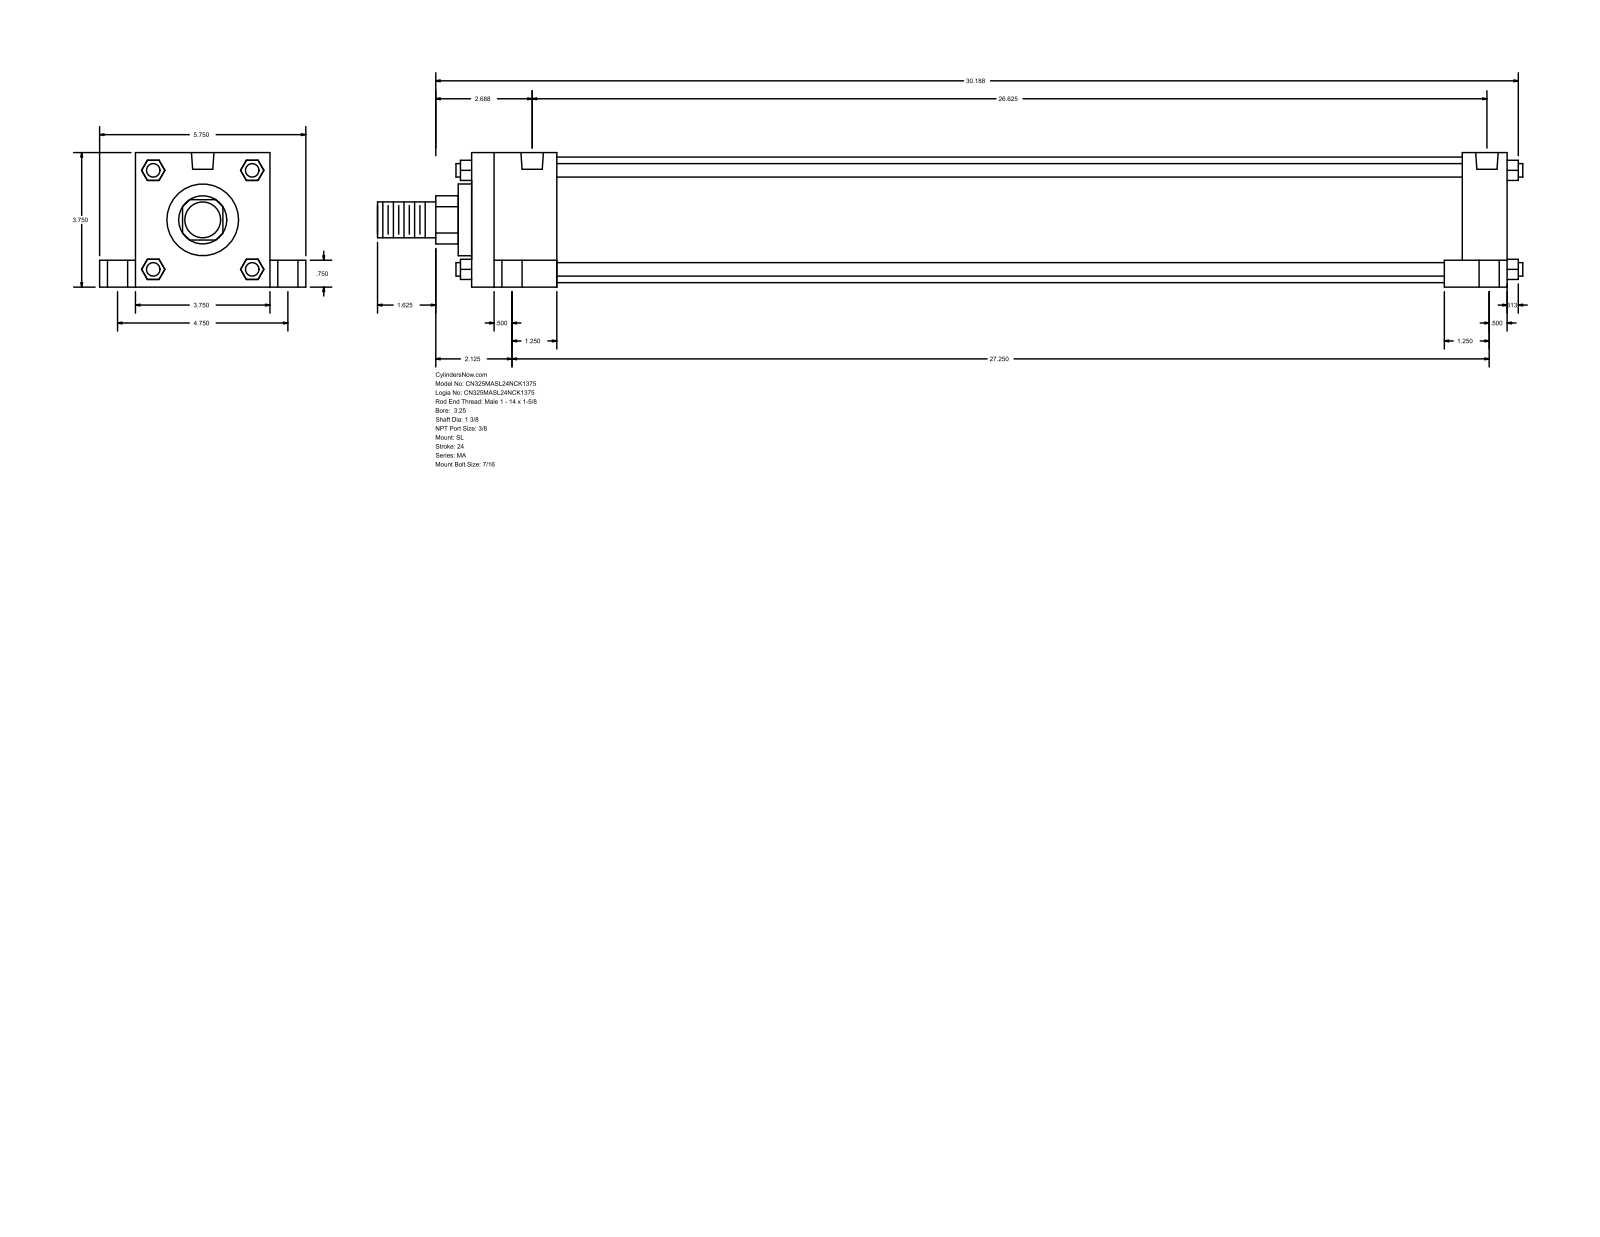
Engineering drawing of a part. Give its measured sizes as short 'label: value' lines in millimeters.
name: MA_SL__0325_1.375
written by: GSSL Pune (CONFIG_CONTROL_DESIGN)
unit: mm
bodies: 0 solids, 148 faces (112 planar, 36 cylindrical, 0 other)
size: 811.21 × 146.05 × 95.25
holes: 4× ⌀11.11, 4× ⌀14.29, 4× ⌀20.64, 2× ⌀15.93
bosses: 4× ⌀9.53, 1× ⌀88.9, 1× ⌀50.8, 1× ⌀34.92, 1× ⌀25.4
rounds: 1× R17.06
face distances: 95.24, 733.43, 25.41, 120.65, 701.68, 31.75, 60.32, 641.36, 673.11, 19.05
hole spacings: 4.77, 60.35, 60.66, 62, 63.27, 120.66, 666.74, 671.51
